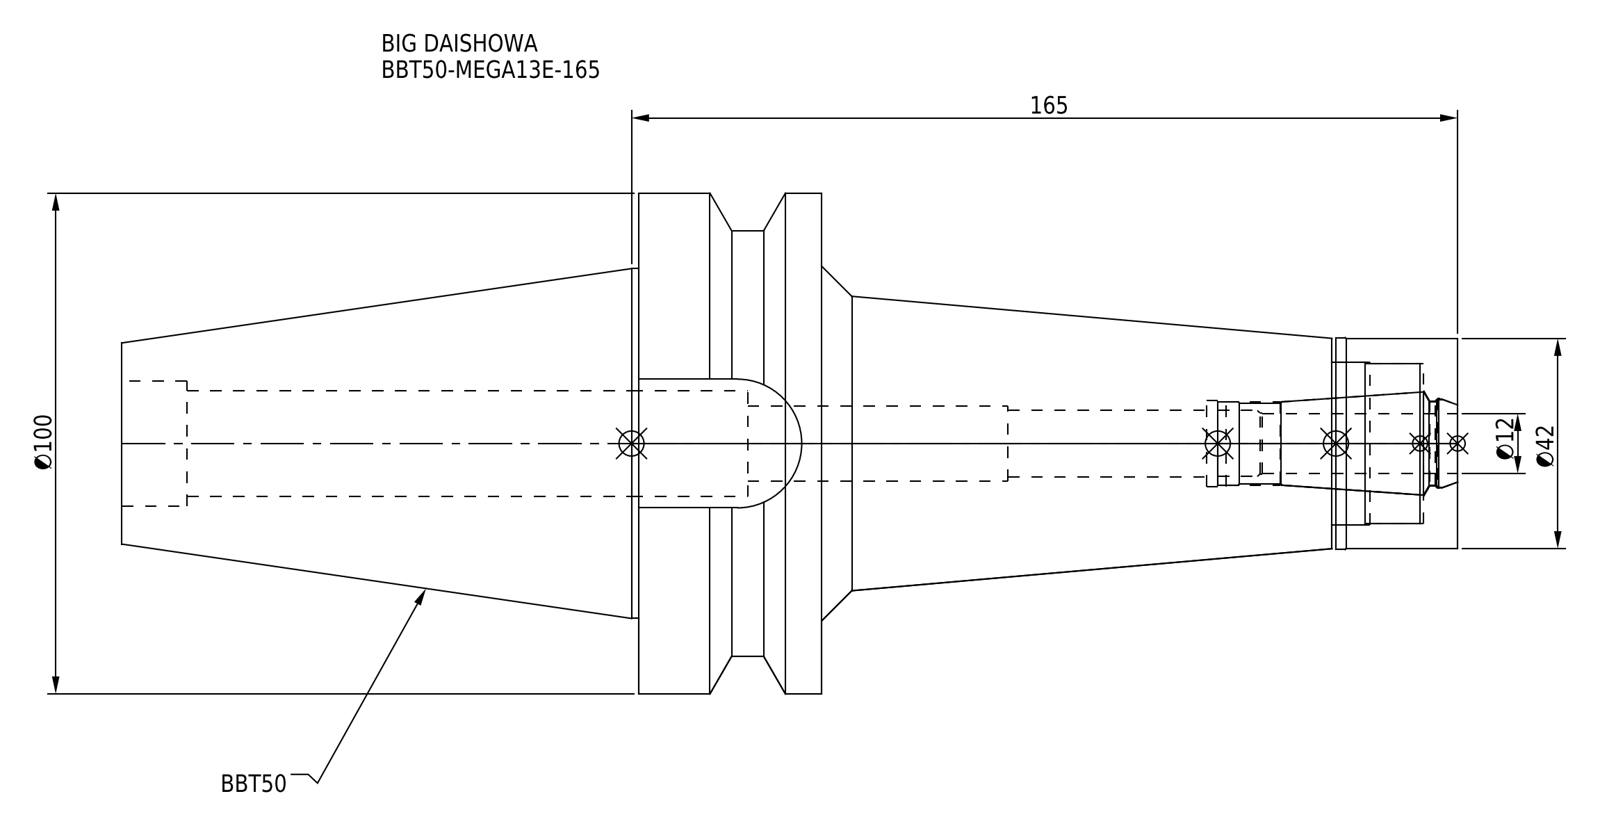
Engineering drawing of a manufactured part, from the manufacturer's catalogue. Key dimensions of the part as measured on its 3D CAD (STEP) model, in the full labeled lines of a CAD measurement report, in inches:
Part name (STEP PRODUCT): BBT50-MEGA13E-165_1.stp; MEN13_1.stp; BBT50ME13165-120_ASM.stp; BBT50-MEGA13E-165-120-FreeParts (+3 more)
STEP written by: SolidWorks 2019 (CONFIG_CONTROL_DESIGN)
Units: inches
Bodies: 2 solids, 81 faces (21 planar, 40 cylindrical, 20 other)
Overall size (bounding box): 10.504 × 3.937 × 3.937
Volume: 41.04 in³ · Surface area: 130 in²
Round holes (diameter × count): ⌀0.524 ×1, ⌀0.591 ×1, ⌀0.654 ×1, ⌀0.669 ×1, ⌀0.677 ×1, ⌀0.705 ×1, ⌀0.835 ×1, ⌀0.984 ×1, ⌀1.26 ×1, ⌀1.28 ×1
Round bosses / shafts (diameter × count): ⌀3.937 ×1, ⌀3.346 ×1, ⌀2.75 ×1, ⌀1.665 ×1, ⌀1.654 ×1
Partial cylindrical surfaces — rounded edges, fillets, slot ends (radius × count): R0.506 ×1
Main face-to-face distances: 1.437, 5, 6.437, 10.504, 5.504, 4.067, 2.787, 0.988, 0.957, 4.043
